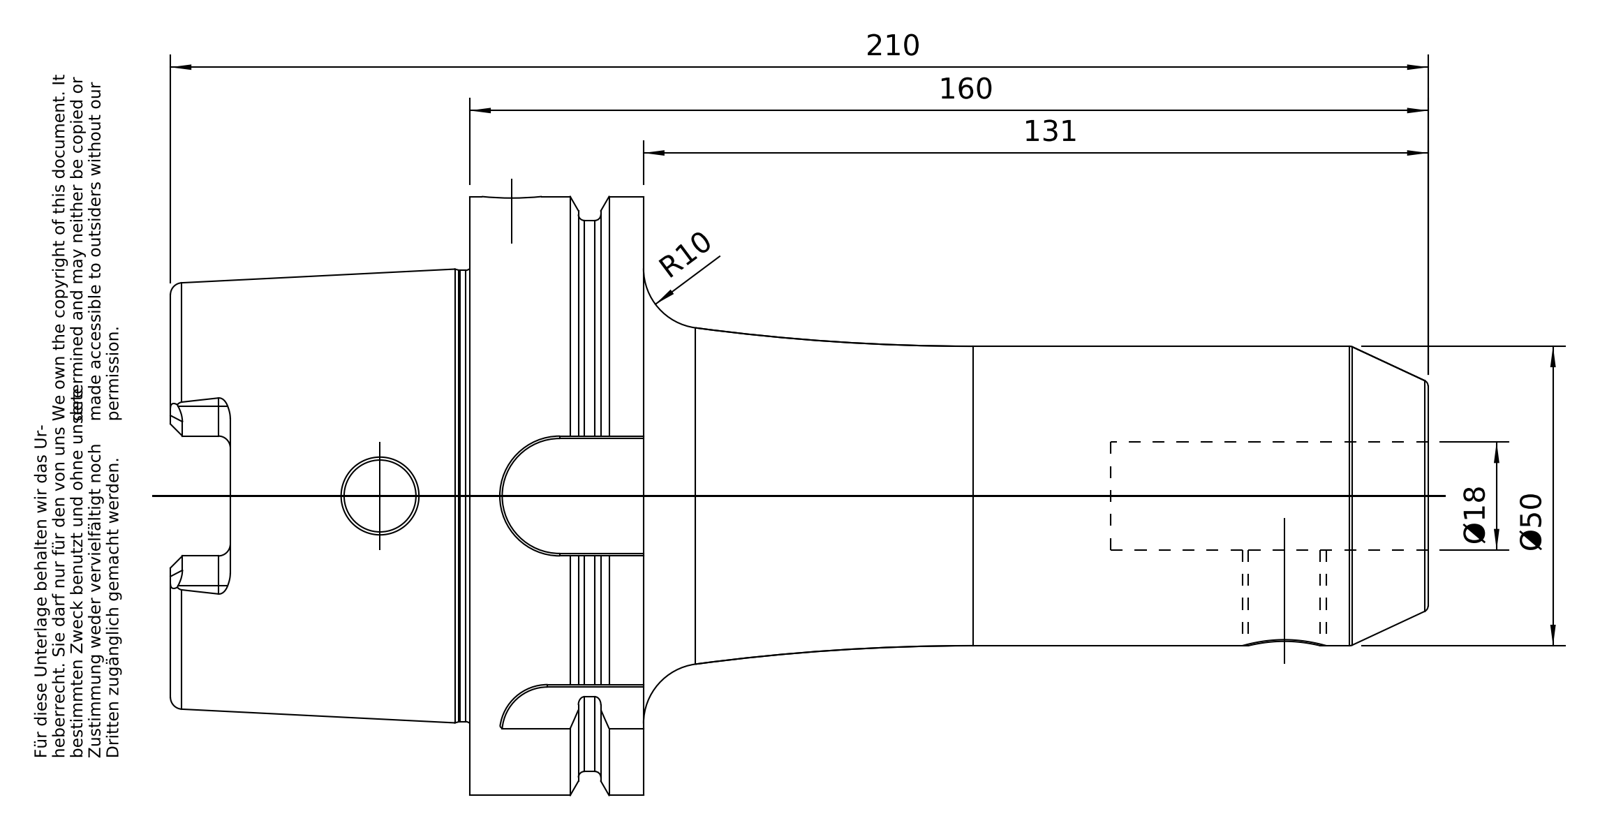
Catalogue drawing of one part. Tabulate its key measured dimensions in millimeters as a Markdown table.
| quantity | value |
| --- | --- |
| part name | A100-002-18 |
| STEP written by | PRO/ENGINEER BY PARAMETRIC TECHNOLOGY CORPORATION, 2010430 (CONFIG_CONTROL_DESIGN) |
| units | millimeters |
| bodies | 1 solid, 182 faces (50 planar, 55 cylindrical, 77 other) |
| overall size | 210 × 100 × 100 |
| volume | 506 624 mm³ |
| surface area | 73 327 mm² |
| round holes (diameter × count) | 12 × 2, 10 × 1, 14 × 1, 18 × 1, 22.5 × 1, 24 × 1, 24.32 × 1, 24.5 × 1, 53 × 1, 63 × 1 |
| round bosses / shafts (diameter × count) | 100 × 1, 92 × 1, 75.36 × 1, 50 × 1 |
| partial cylindrical surfaces (radius × count) | 2 × 6, 5 × 4, 8 × 1, 10 × 1, 11 × 1 |
| main face-to-face distances | 29, 12.5, 16.5, 50, 62.5, 79, 210, 160, 147.5, 131 |
| hole center spacings | 129 |
